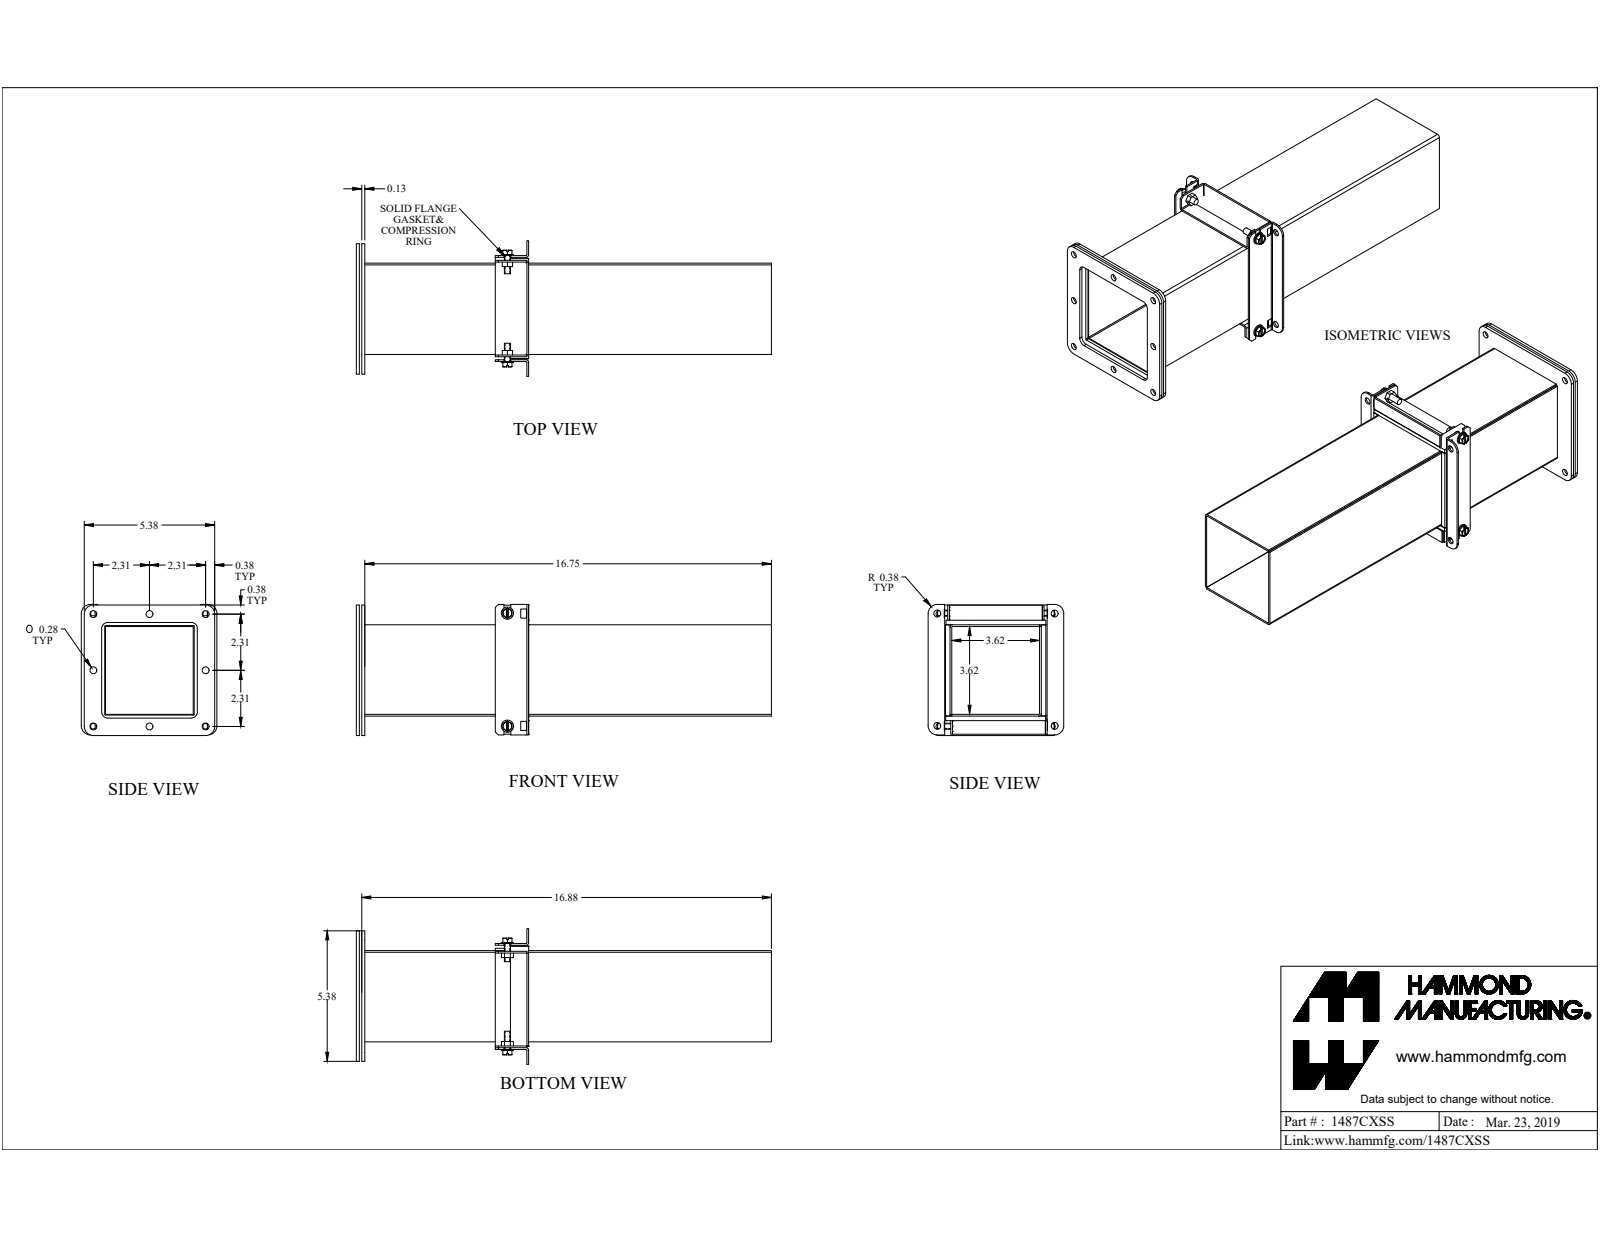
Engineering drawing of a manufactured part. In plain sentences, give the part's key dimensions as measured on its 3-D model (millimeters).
The part is named "1487CXSS". Its 3-D file was written by "SolidWorks 2019 (CONFIG_CONTROL_DESIGN)". It is 23 solids with 479 faces: 309 planar, 130 cylindrical and 40 other. Overall it measures 443.1 by 141.9 by 137.1 millimeters. Its volume is 432 300 cubic millimeters and its surface area 439 700 square millimeters. Round holes: 14 of diameter 7.1, 3 of diameter 5, 3 of diameter 8.9, 1 of diameter 6.6. Round bosses or shafts: 3 of diameter 12.7, 3 of diameter 6.4. Partial cylindrical surfaces (rounded edges, fillets, slot ends): 26 of radius 0.5, 10 of radius 0.9, 10 of radius 2.7, 8 of radius 9.5, 4 of radius 0.8, 4 of radius 6.4. The main face-to-face distances are 1.8, 1.8, 95.5, 93.7, 91.8, 93.7, 3.2, 5.7, 8, 2.5. The hole center spacings are 58.8, 131.3, 117.5, 83.1, 3.1, 61, 61.8, 117.5.
